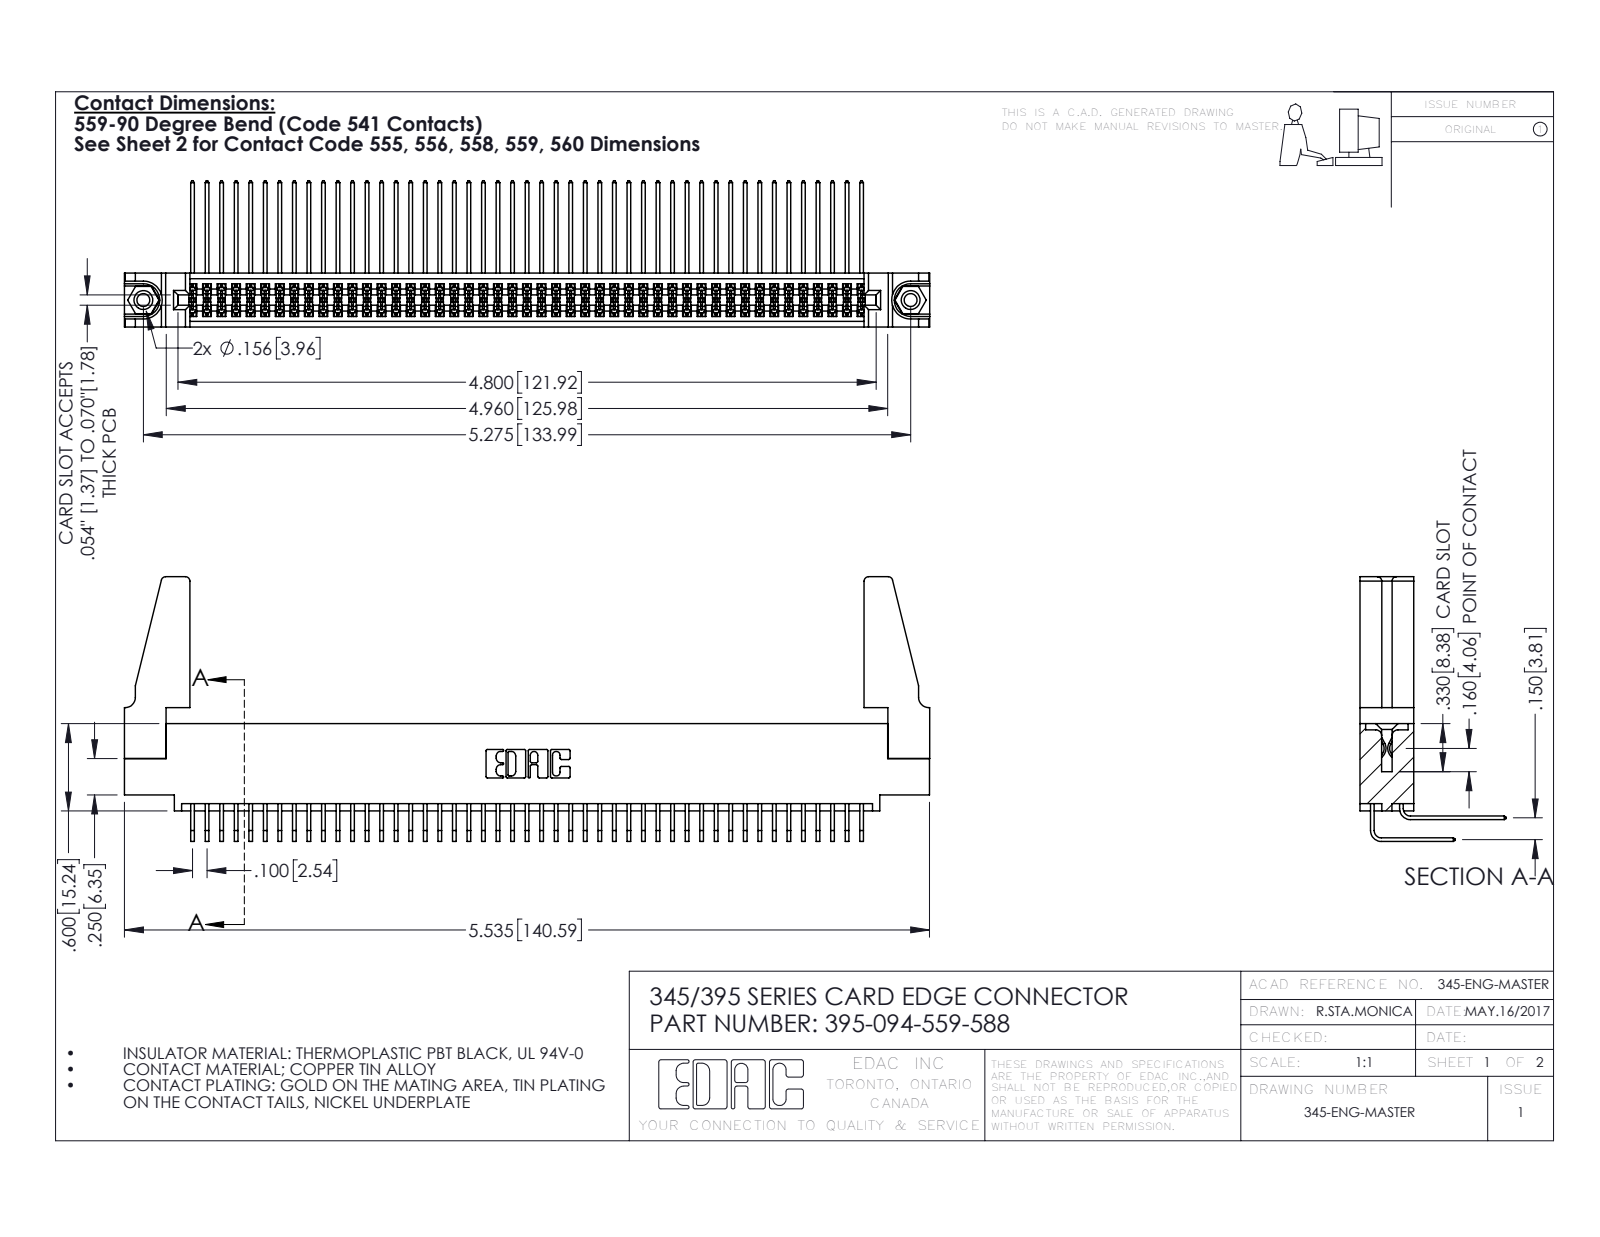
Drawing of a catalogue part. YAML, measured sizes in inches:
part_name: "395-094-559-588; 345 Part_0.110 Offset - 0.156 Dia-TH; 345-292-001_558 559 Tail - 1; 345-250-001_345-250-001-102 (+2 more)"
step_written_by: "SolidWorks 2016 (CONFIG_CONTROL_DESIGN)"
units: inches
bodies: {solids: 99, faces: 5142, planar: 3446, cylindrical: 1680, other: 16}
overall_size: [5.536, 1.819, 1.005]
volume: 1.063
surface_area: 41.56
round_holes:
  - {diameter: 0.089, count: 2}
  - {diameter: 0.125, count: 2}
  - {diameter: 0.156, count: 2}
  - {diameter: 0.064, count: 1}
round_bosses_or_shafts:
  - {diameter: 0.155, count: 2}
partial_cylinders:
  - {radius: 0.006, count: 141}
  - {radius: 0.01, count: 22}
  - {radius: 0.03, count: 8}
  - {radius: 0.007, count: 6}
  - {radius: 0.031, count: 6}
  - {radius: 0.026, count: 3}
  - {radius: 0.014, count: 2}
  - {radius: 0.019, count: 2}
face_to_face_distances: [0.072, 0.298, 0.37, 0.2, 0.098, 0.272, 0.025, 0.225, 0.175, 0.15]
hole_center_spacings: [0.27, 5.039, 5.275]
